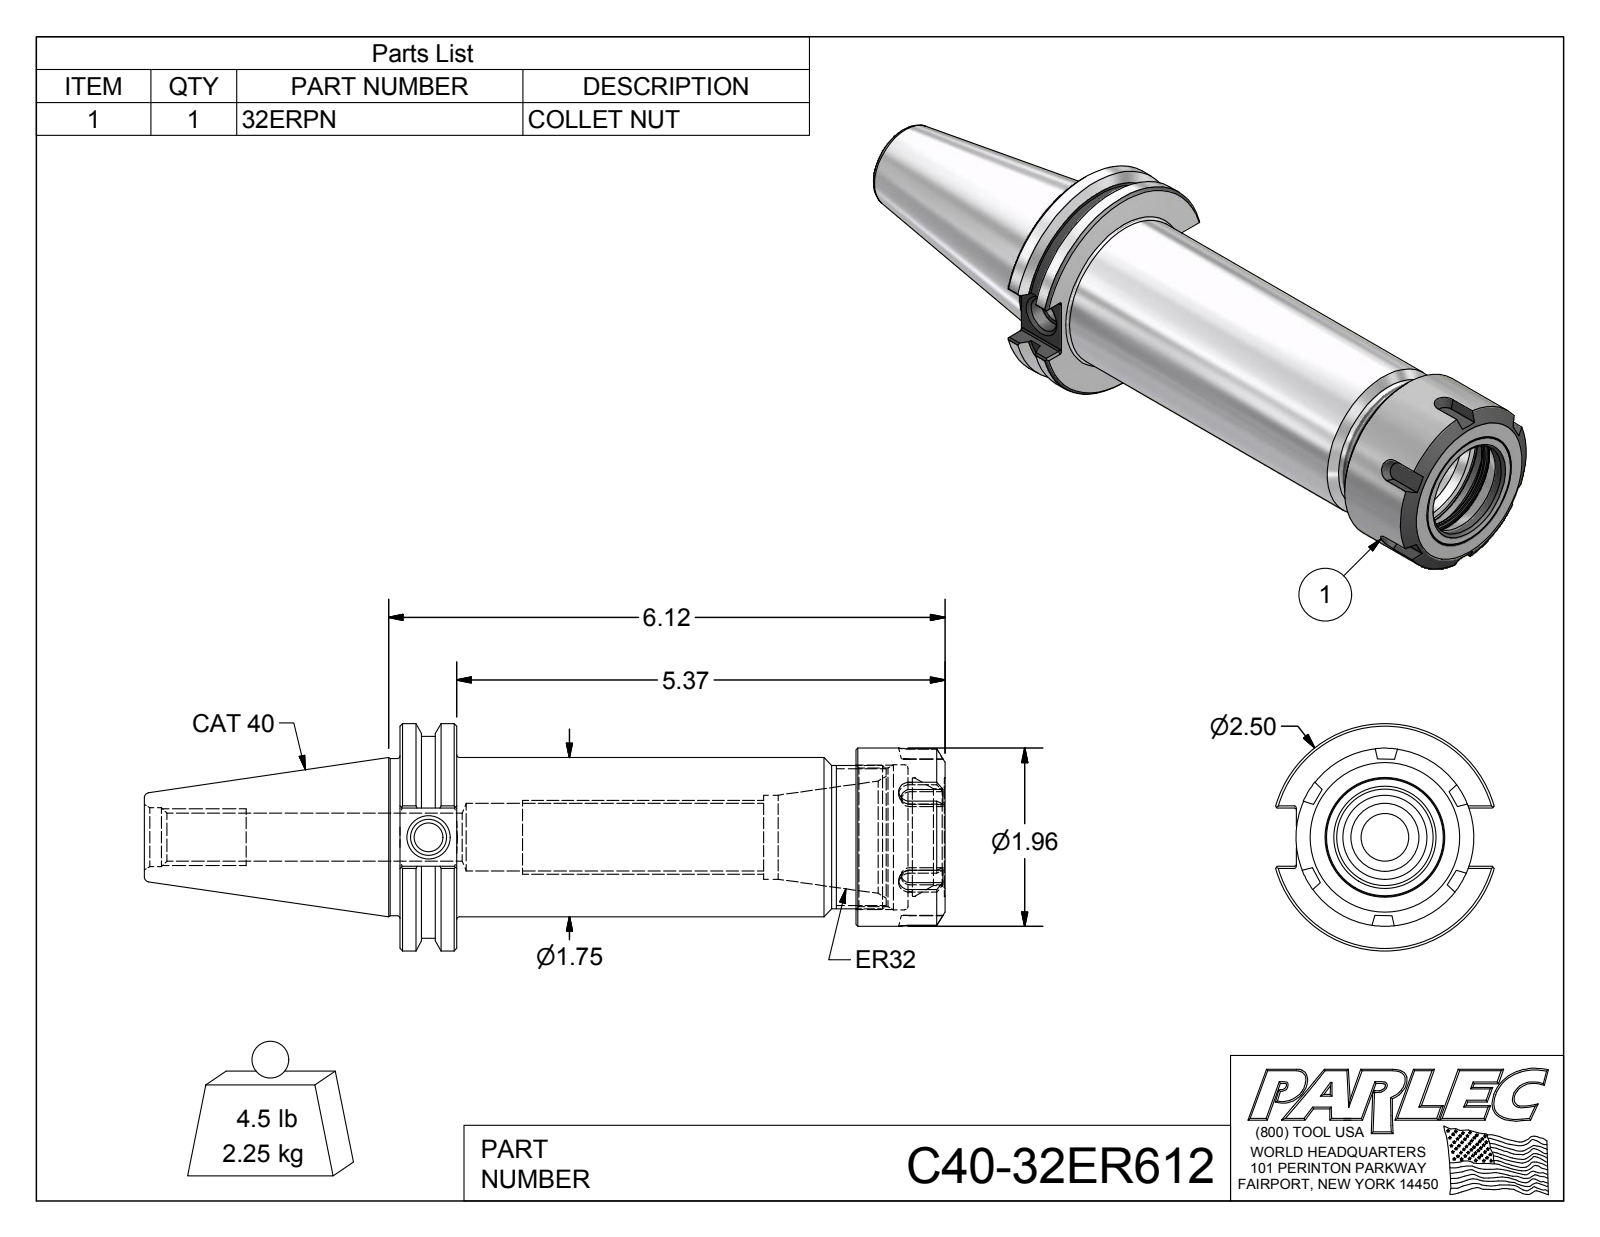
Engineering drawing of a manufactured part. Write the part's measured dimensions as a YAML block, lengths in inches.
part_name: "C40-32ER612; C40-32ER6-1; 32ERPN"
step_written_by: "Autodesk Inventor 2012 (AUTOMOTIVE_DESIGN)"
units: inches
bodies: {solids: 2, faces: 129, planar: 55, cylindrical: 33, other: 41}
overall_size: [8.808, 2.5, 2.403]
volume: 15.83
surface_area: 82.66
round_holes:
  - {diameter: 0.315, count: 1}
  - {diameter: 0.399, count: 1}
  - {diameter: 0.527, count: 1}
  - {diameter: 0.648, count: 1}
  - {diameter: 0.745, count: 1}
  - {diameter: 0.925, count: 1}
  - {diameter: 1.063, count: 1}
  - {diameter: 1.2, count: 1}
  - {diameter: 1.305, count: 1}
  - {diameter: 1.523, count: 1}
  - {diameter: 1.595, count: 1}
round_bosses_or_shafts:
  - {diameter: 2.5, count: 1}
  - {diameter: 2.219, count: 1}
  - {diameter: 1.958, count: 1}
  - {diameter: 1.75, count: 1}
  - {diameter: 1.73, count: 1}
  - {diameter: 1.575, count: 1}
partial_cylinders:
  - {radius: 0.02, count: 12}
face_to_face_distances: [0.625, 5.995, 5.37, 5.017, 4.392, 0.978, 5.588, 4.963, 0.571, 0.407]
